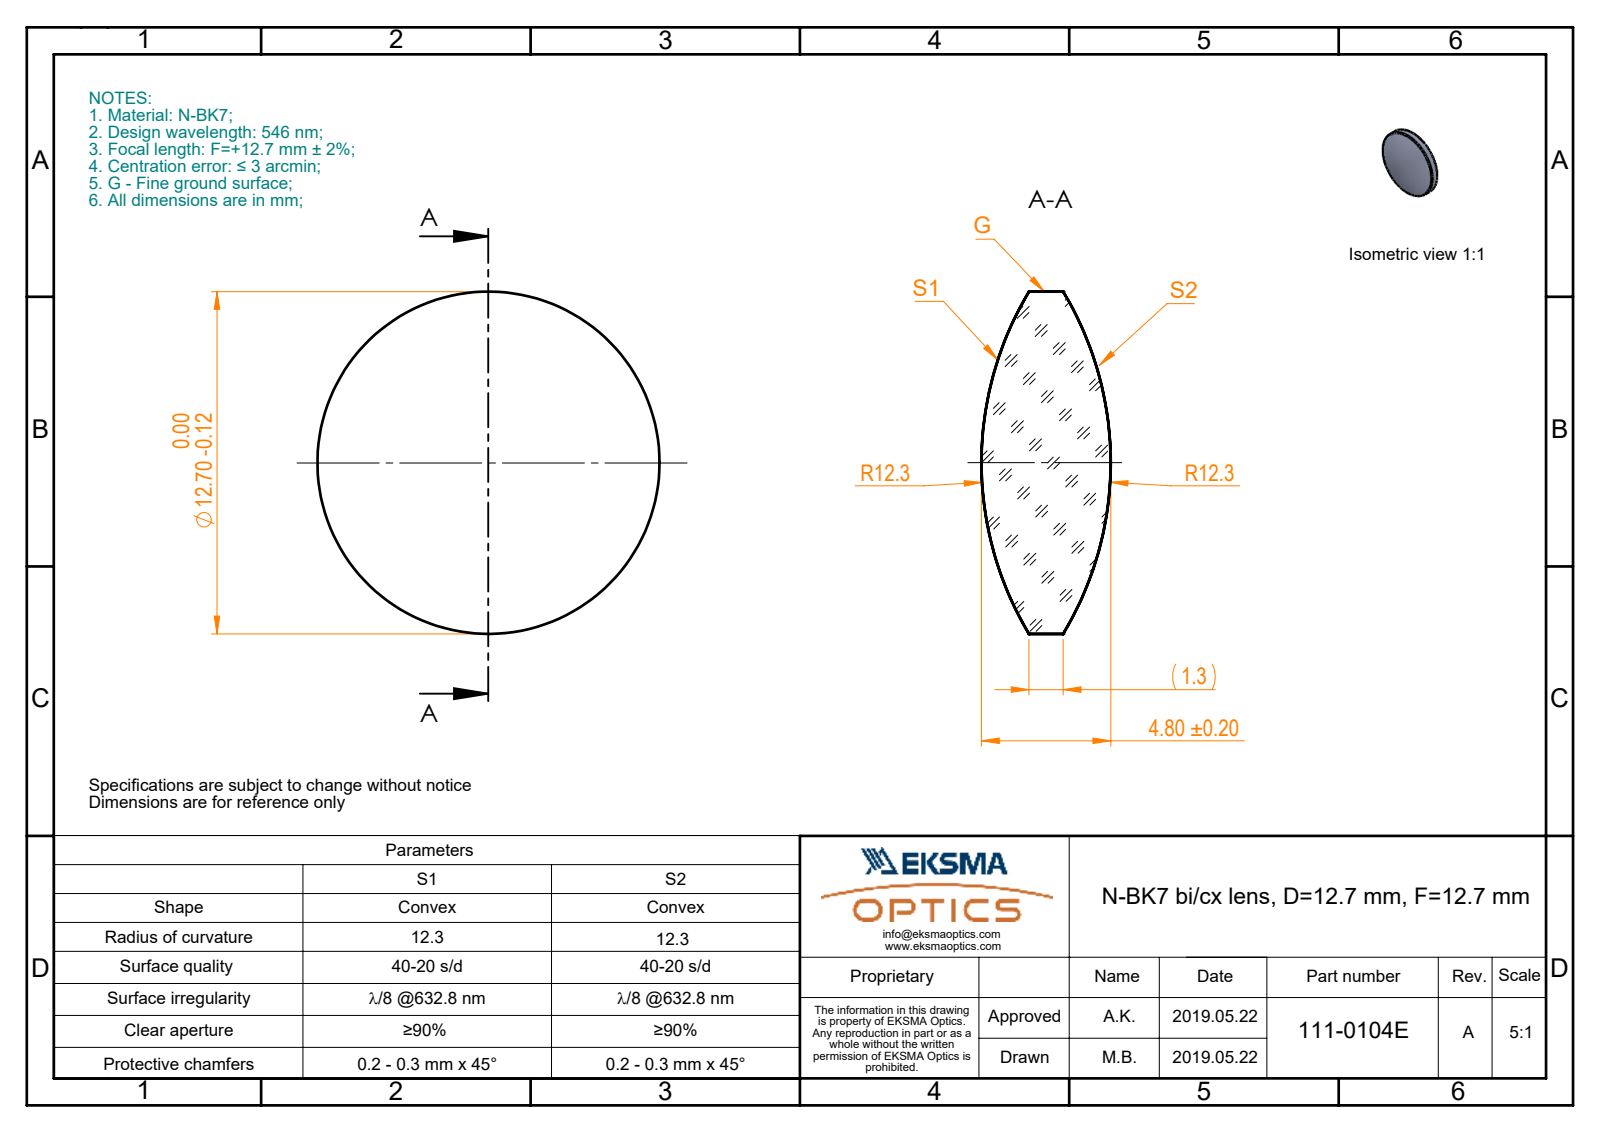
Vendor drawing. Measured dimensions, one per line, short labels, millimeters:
name: 111-0104E BK7 bi-cx 12.7 F12.7
written by: SolidWorks 2017 (CONFIG_CONTROL_DESIGN)
unit: mm
bodies: 1 solid, 6 faces (0 planar, 2 cylindrical, 4 other)
size: 12.7 × 12.7 × 4.8
volume: 390 mm³; area: 324 mm²
bosses: 1× ⌀12.7
